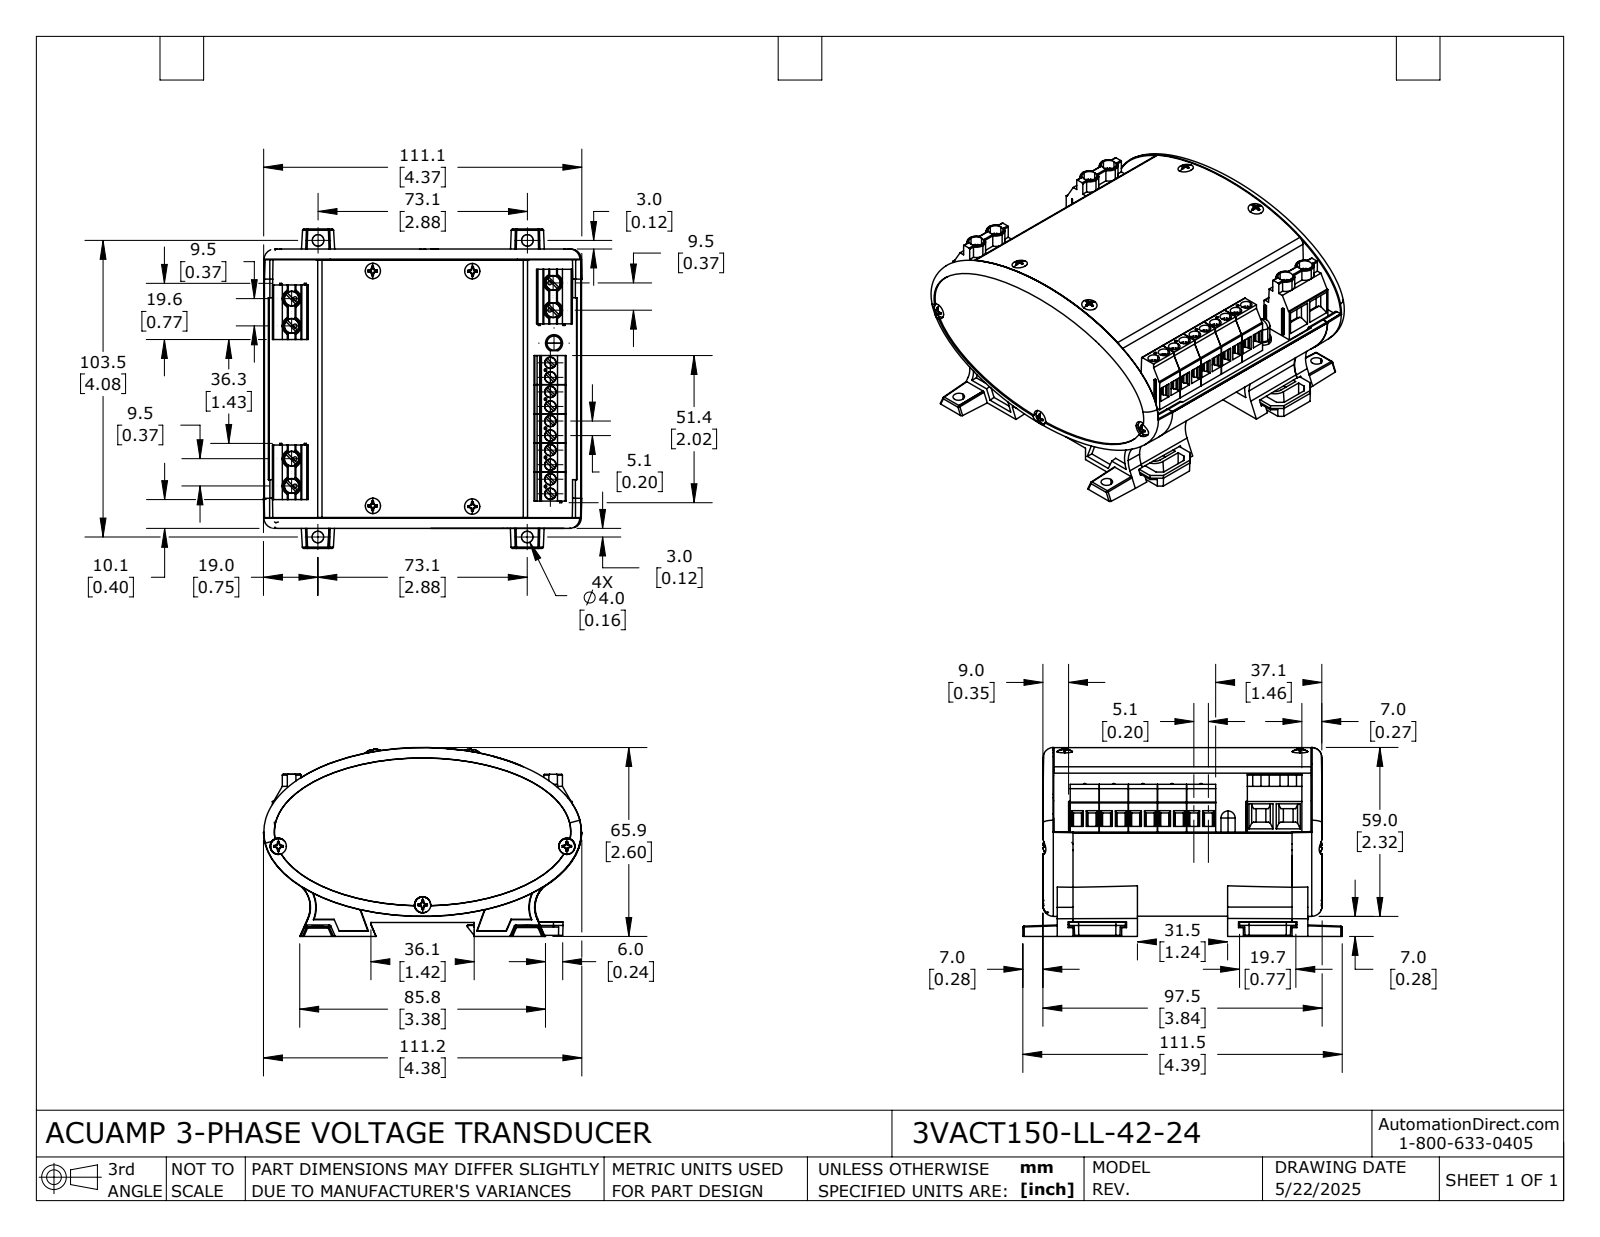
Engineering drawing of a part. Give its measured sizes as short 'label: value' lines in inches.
name: 3VACT150-LL-42-24
written by: SolidWorks 2024 (AUTOMOTIVE_DESIGN)
unit: in
bodies: 26 solids, 2965 faces (1484 planar, 838 cylindrical, 643 other)
size: 4.391 × 4.377 × 2.597
volume: 8.539 in³; area: 197.4 in²
holes: 12× ⌀0.05, 10× ⌀0.157, 6× ⌀0.08, 6× ⌀0.111, 6× ⌀0.205, 4× ⌀0.126
bosses: 16× ⌀0.051, 10× ⌀0.15, 10× ⌀0.112, 10× ⌀0.067, 6× ⌀0.197, 4× ⌀0.018, 1× ⌀0.234, 1× ⌀0.194
rounds: 40× R0.006, 20× R0.039, 16× R0.008, 16× R0.02, 6× R0.01, 6× R0.012, 6× R0.128, 4× R0.018
face distances: 0.063, 0.128, 3.672, 3.8, 3.543, 0.084, 0.394, 3.406, 0.266, 3.278
hole spacings: 0.2, 0.4, 0.6, 0.8, 1, 1.2, 1.4, 1.6
